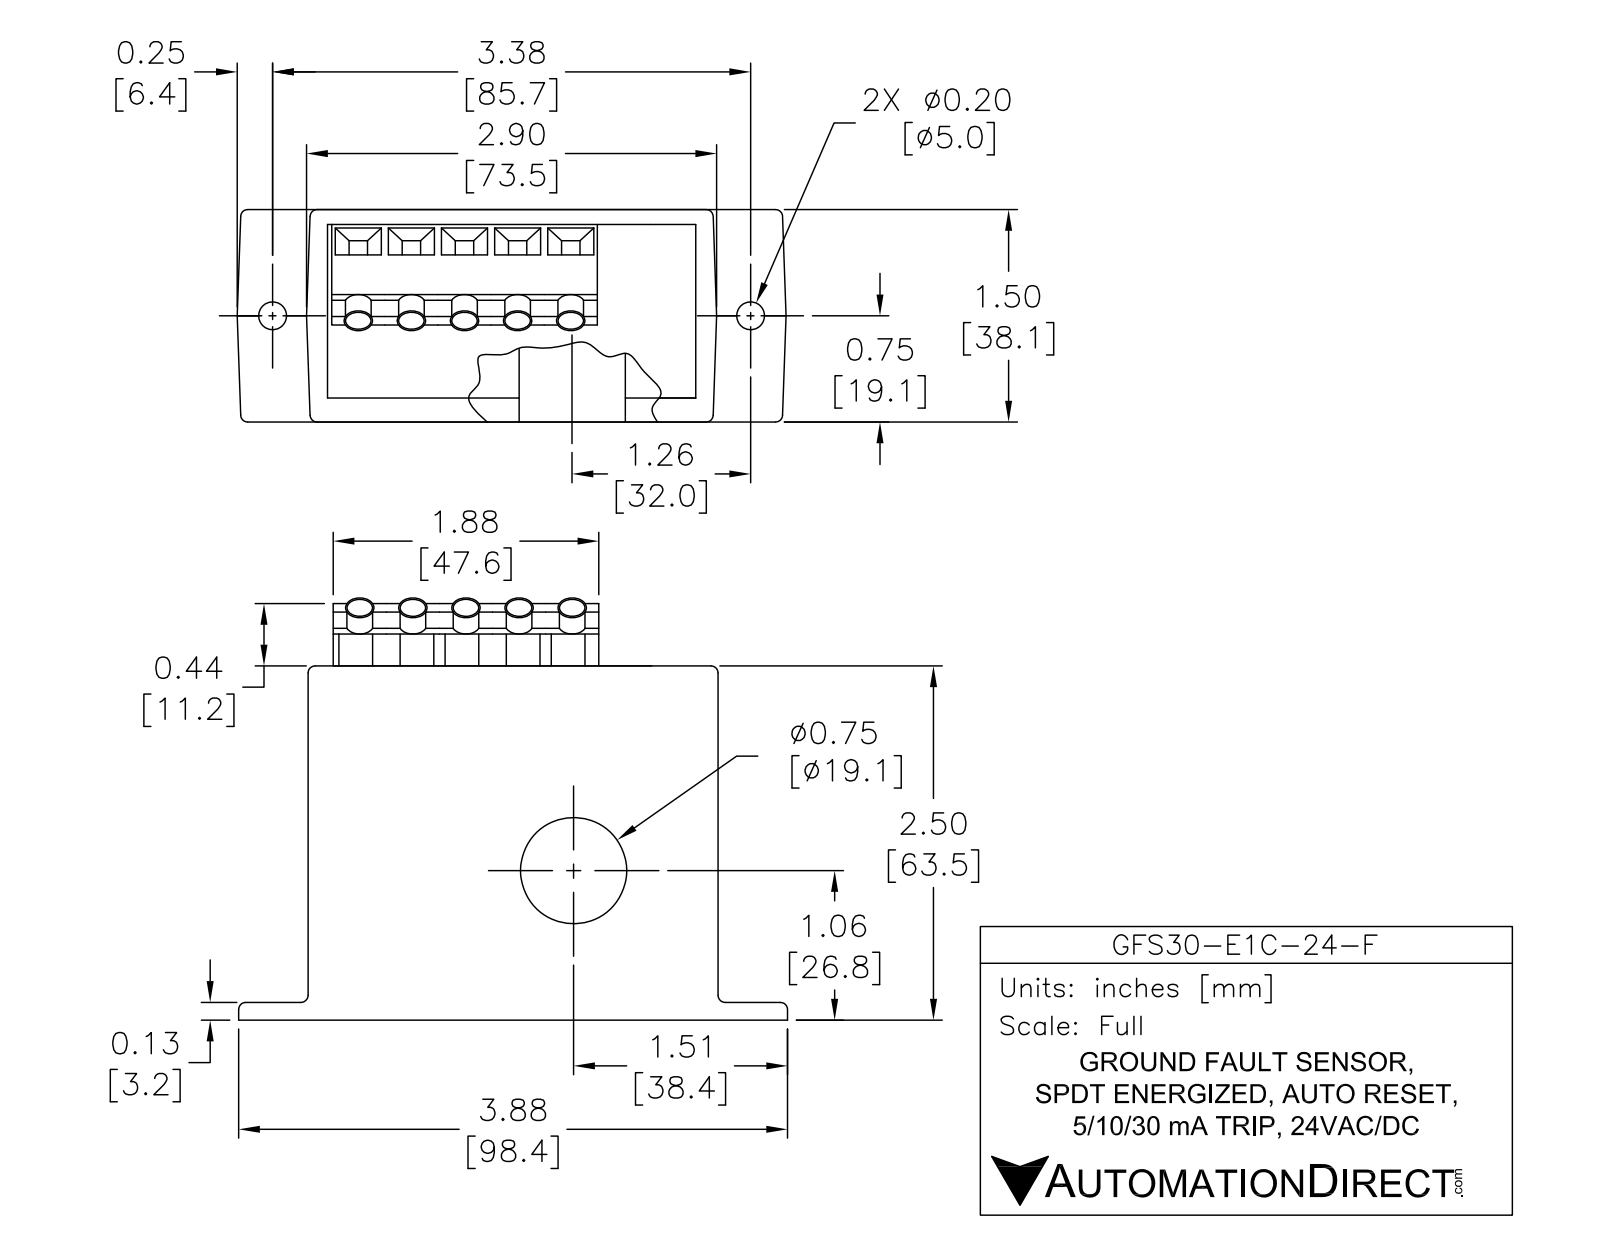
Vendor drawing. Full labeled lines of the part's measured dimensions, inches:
Part name (STEP PRODUCT): GFS30-E1C-24-F
STEP written by: SolidWorks 2019 (AUTOMOTIVE_DESIGN)
Units: inches
Bodies: 20 solids, 318 faces (265 planar, 49 cylindrical, 4 other)
Overall size (bounding box): 3.875 × 2.908 × 1.504
Volume: 10.52 in³ · Surface area: 53.65 in²
Round holes (diameter × count): ⌀0.206 ×5, ⌀0.196 ×2, ⌀0.2 ×2, ⌀0.75 ×1
Round bosses / shafts (diameter × count): ⌀0.186 ×5
Partial cylindrical surfaces — rounded edges, fillets, slot ends (radius × count): R0.128 ×5
Main face-to-face distances: 1.5, 2.455, 2.895, 0.1, 2.355, 1.504, 0.104, 2.459, 0.045, 0.125
Hole centre spacings: 0.748, 0.354, 0.394, 0.37, 0.681, 1.022, 1.102, 1.142
